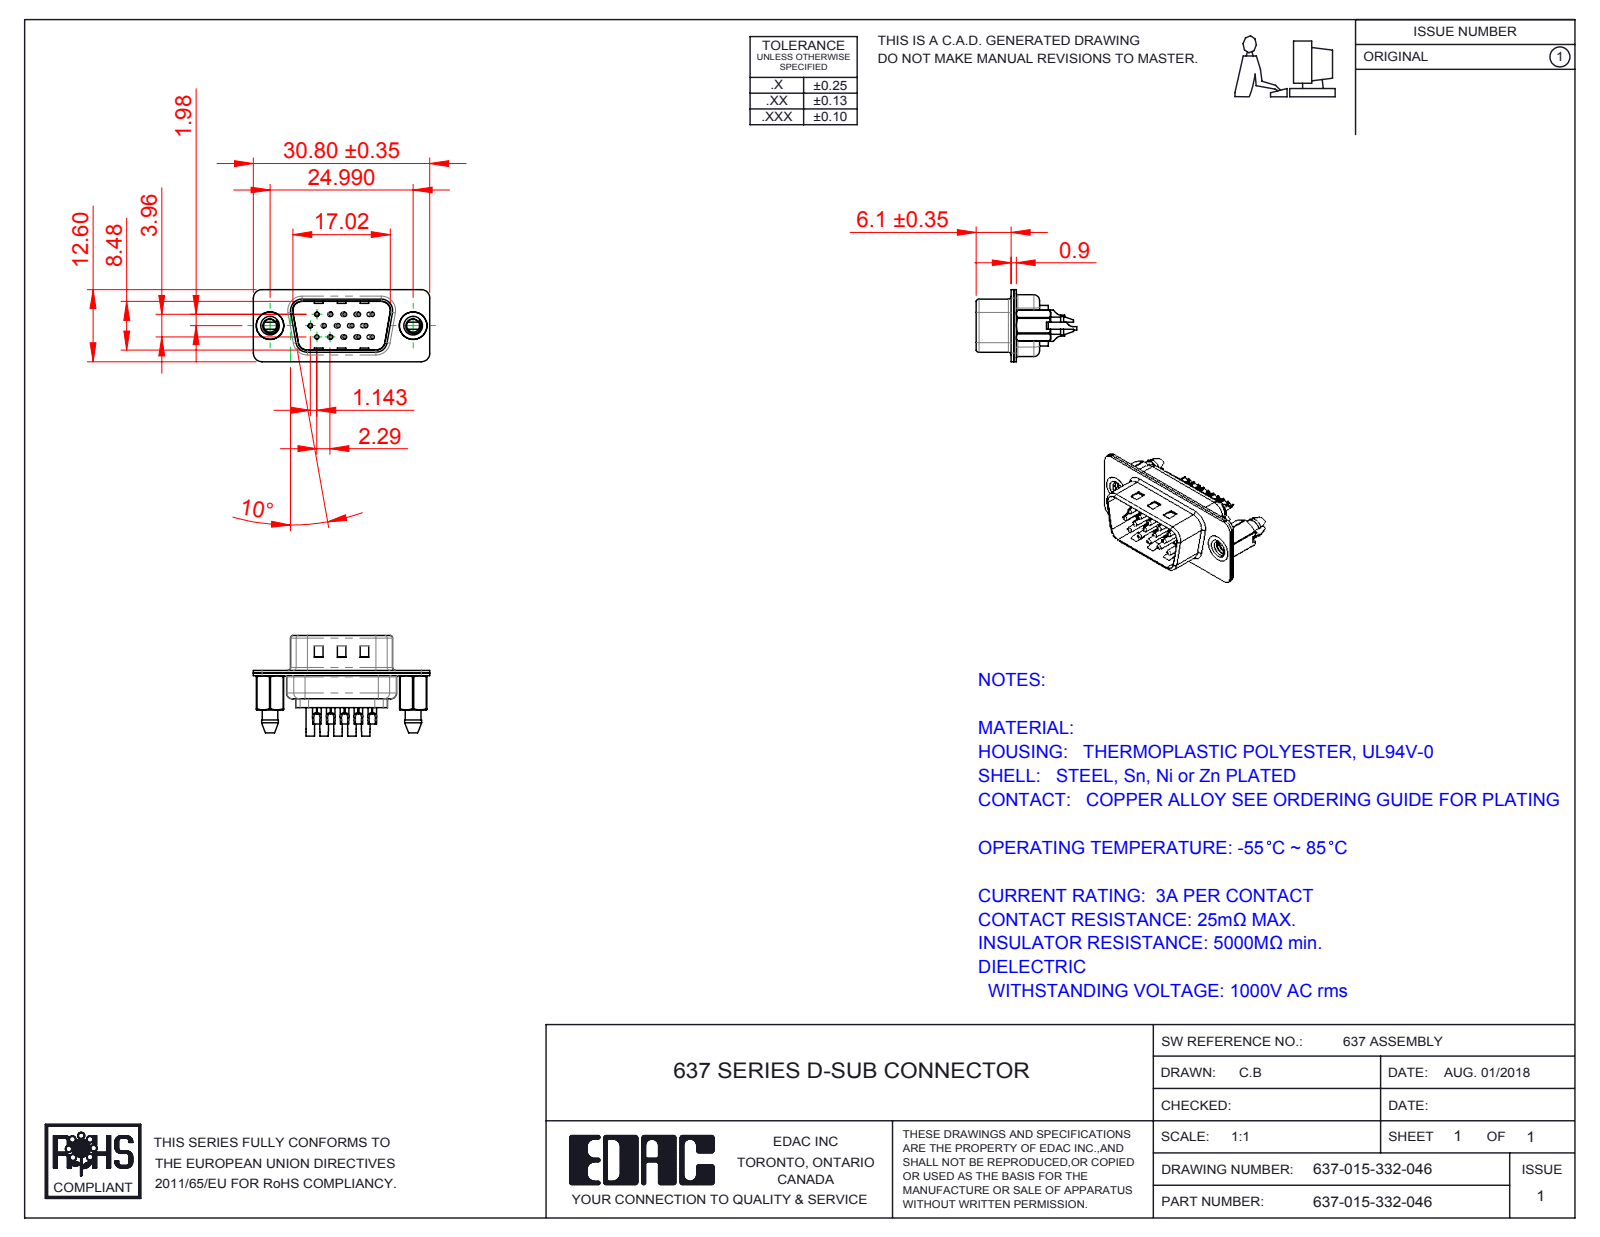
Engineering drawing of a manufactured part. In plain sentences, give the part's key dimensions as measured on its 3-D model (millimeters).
The part is named "637-015-332-046; 637 4-40 Threaded Boardlock_LP; 637 Contact Row 3_32; 637 Contact Row 2_32 (+4 more)". Its 3-D file was written by "SolidWorks 2016 (CONFIG_CONTROL_DESIGN)". It is 20 solids with 1338 faces: 349 planar, 596 cylindrical and 393 other. Overall it measures 30.8 by 17.55 by 12.6 millimeters. Its volume is 1 444 cubic millimeters and its surface area 5 064 square millimeters. Round holes: 27 of diameter 1.6, 15 of diameter 0.35, 15 of diameter 1.1, 12 of diameter 0.75, 12 of diameter 2, 2 of diameter 2.26, 2 of diameter 4, 2 of diameter 4.8. Round bosses or shafts: 15 of diameter 2, 15 of diameter 1.5, 15 of diameter 0.75, 2 of diameter 4.9. Partial cylindrical surfaces (rounded edges, fillets, slot ends): 18 of radius 1.5, 12 of radius 2, 8 of radius 0.5, 7 of radius 1, 6 of radius 1.6, 4 of radius 0.25, 4 of radius 0.55, 4 of radius 0.7. The main face-to-face distances are 0.45, 0.4, 0.9, 0.7, 8.48, 8.88, 6.5, 4.55, 0.31, 1.95. The hole center spacings are 3.96, 2.29, 2.28, 4.57, 2.42, 6.05, 4.84, 2.35.
